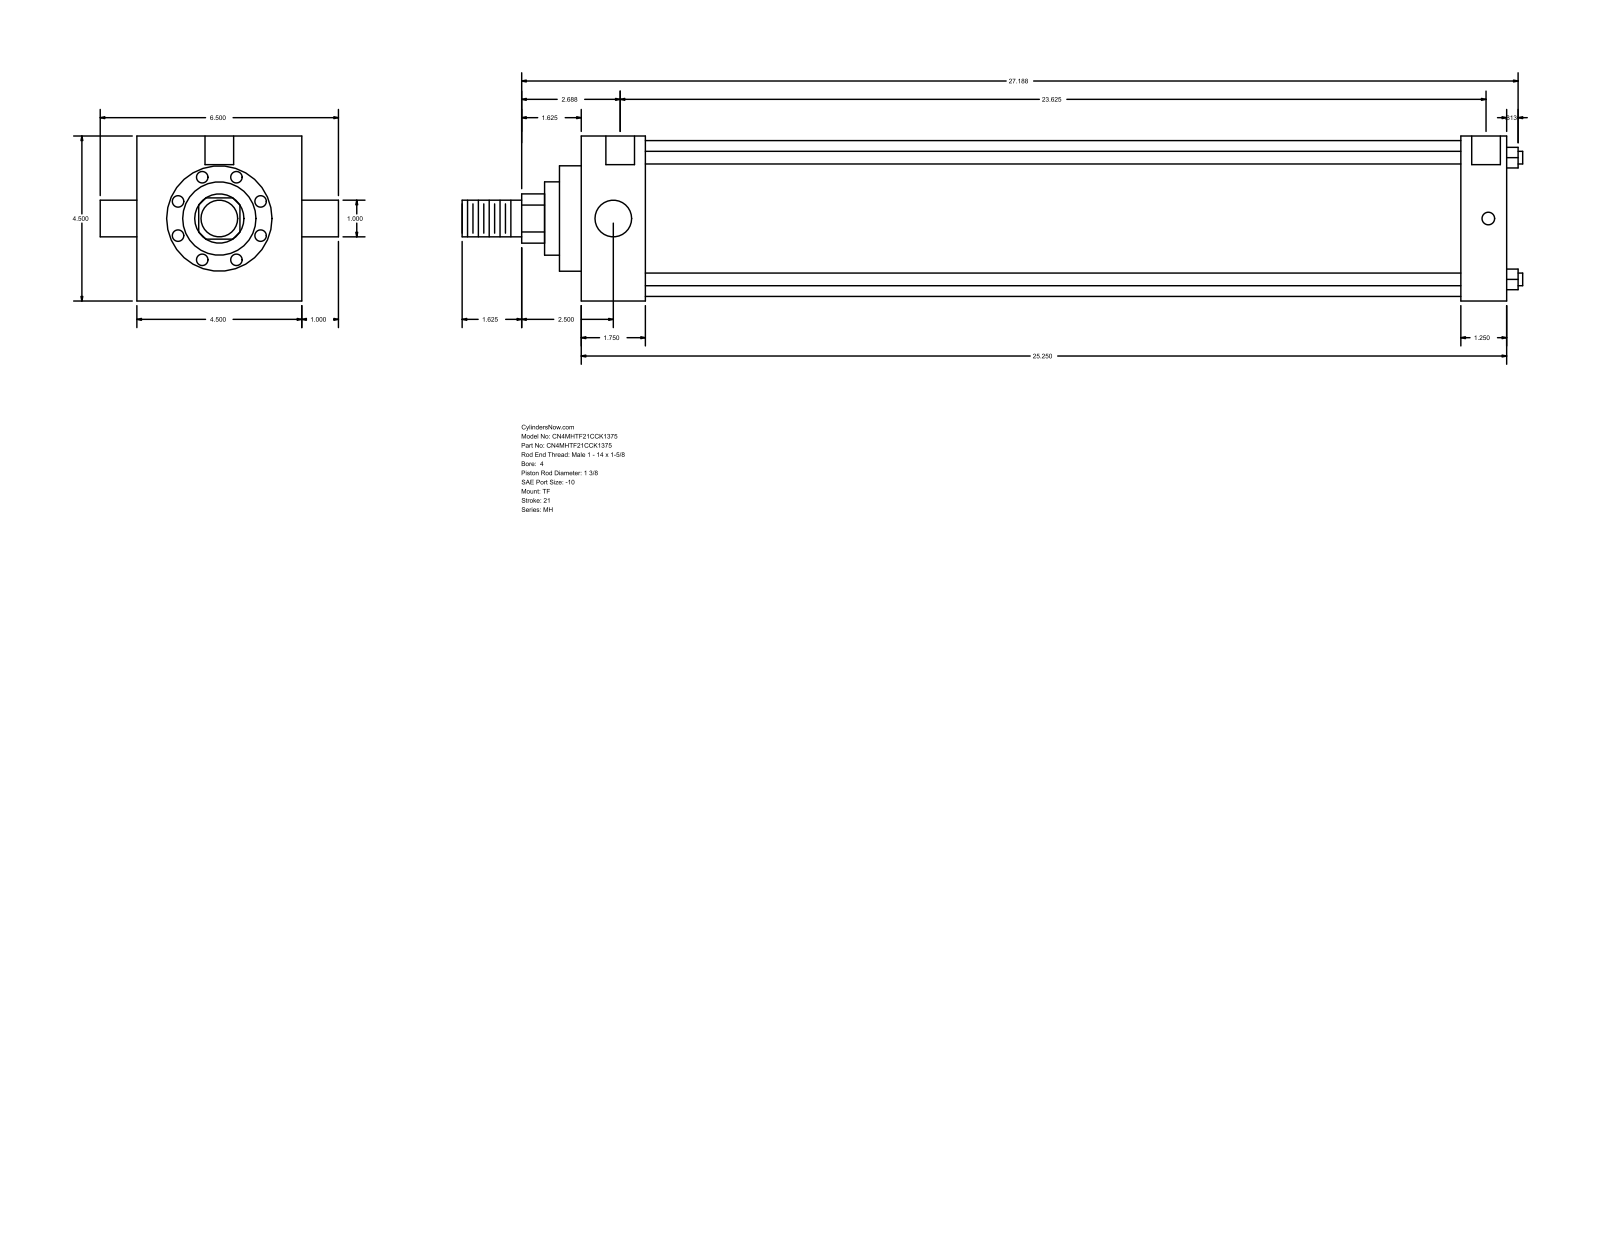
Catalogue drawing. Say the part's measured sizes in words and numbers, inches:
The part is named "MH_TF__0400_1.375". Its 3-D file was written by "GSSL Pune (CONFIG_CONTROL_DESIGN)". It is 0 solids with 86 faces: 61 planar, 25 cylindrical and 0 other. Overall it measures 28.937 by 6.5 by 4.5 inches. Round holes: 3 of diameter 0.344, 2 of diameter 0.781. Round bosses or shafts: 4 of diameter 0.345, 2 of diameter 1, 1 of diameter 4.25, 1 of diameter 2.875, 1 of diameter 2, 1 of diameter 1.375. Partial cylindrical surfaces (rounded edges, fillets, slot ends): 1 of radius 0.672. The main face-to-face distances are 4.5, 25.25, 1.75, 23.5, 24, 22.25, 1.25, 0.594, 2.344, 24.594. The hole center spacings are 0.062, 0.063, 23.625, 23.687, 23.688, 23.75.
